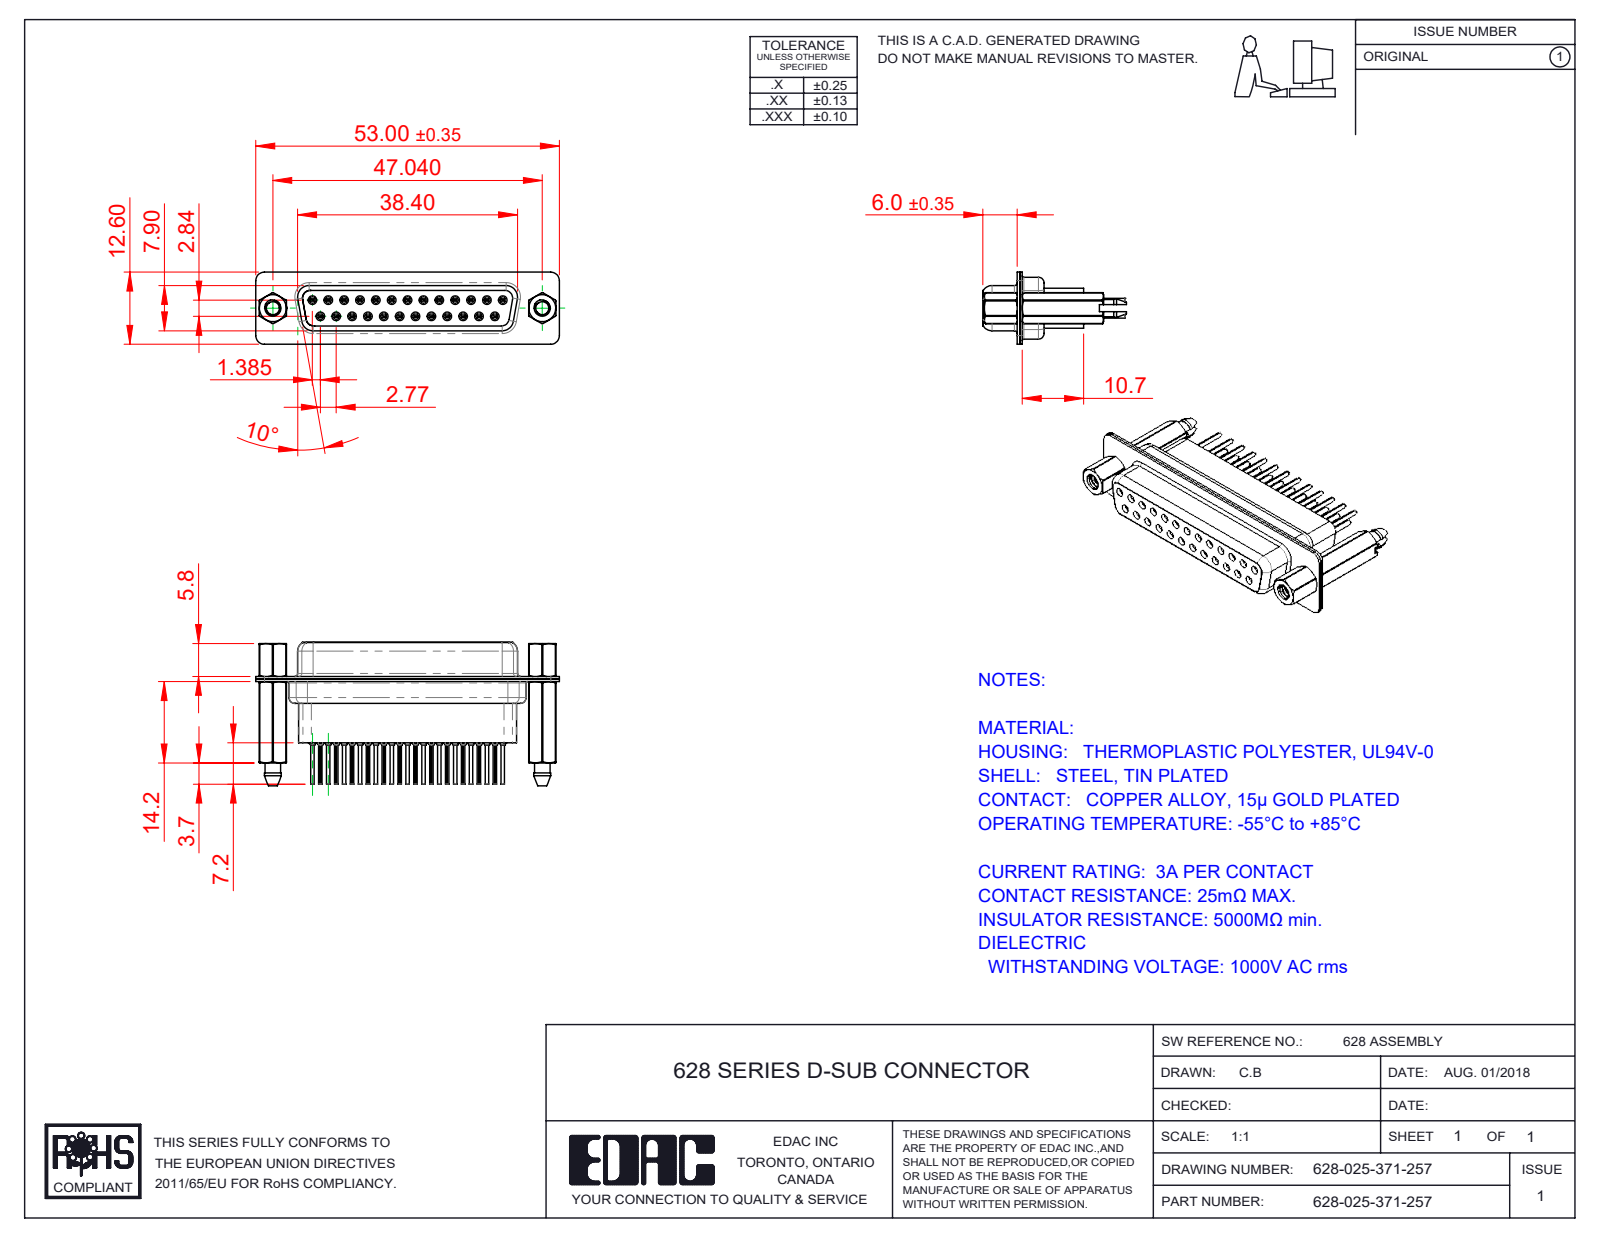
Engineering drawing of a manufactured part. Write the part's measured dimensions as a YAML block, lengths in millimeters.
part_name: "628 Shell Rear_25 Contacts; 628 Contact Row 1_71; 628 4-40 Threaded Boardlock_HP71; 628 Contact Row 2_71 (+4 more)"
step_written_by: "SolidWorks 2020 (CONFIG_CONTROL_DESIGN)"
units: millimeters
bodies: {solids: 32, faces: 3554, planar: 896, cylindrical: 1066, other: 1592}
overall_size: [53, 25.1, 12.6]
volume: 5587
surface_area: 12849
round_holes:
  - {diameter: 0.2, count: 25}
  - {diameter: 0.8, count: 25}
  - {diameter: 0.9, count: 25}
  - {diameter: 1.1, count: 25}
  - {diameter: 1.6, count: 25}
  - {diameter: 1.7, count: 13}
  - {diameter: 2.26, count: 2}
  - {diameter: 2.29, count: 2}
  - {diameter: 4, count: 2}
  - {diameter: 4.05, count: 2}
  - {diameter: 4.85, count: 2}
round_bosses_or_shafts:
  - {diameter: 2, count: 25}
  - {diameter: 1.5, count: 25}
  - {diameter: 1.2, count: 25}
  - {diameter: 0.6, count: 25}
  - {diameter: 4.95, count: 2}
  - {diameter: 4.8, count: 2}
  - {diameter: 2.79, count: 2}
partial_cylinders:
  - {radius: 0.1, count: 50}
  - {radius: 0.28, count: 25}
  - {radius: 1.5, count: 18}
  - {radius: 2, count: 12}
  - {radius: 1.35, count: 6}
  - {radius: 1.6, count: 6}
  - {radius: 0.25, count: 4}
  - {radius: 0.5, count: 4}
face_to_face_distances: [0.45, 0.4, 6.6, 8.5, 1.9, 7, 0.9, 4.76, 1.4, 7.05]
hole_center_spacings: [3.16, 8.31, 2.77, 5.54, 11.08, 16.62, 5.03, 5.04]
